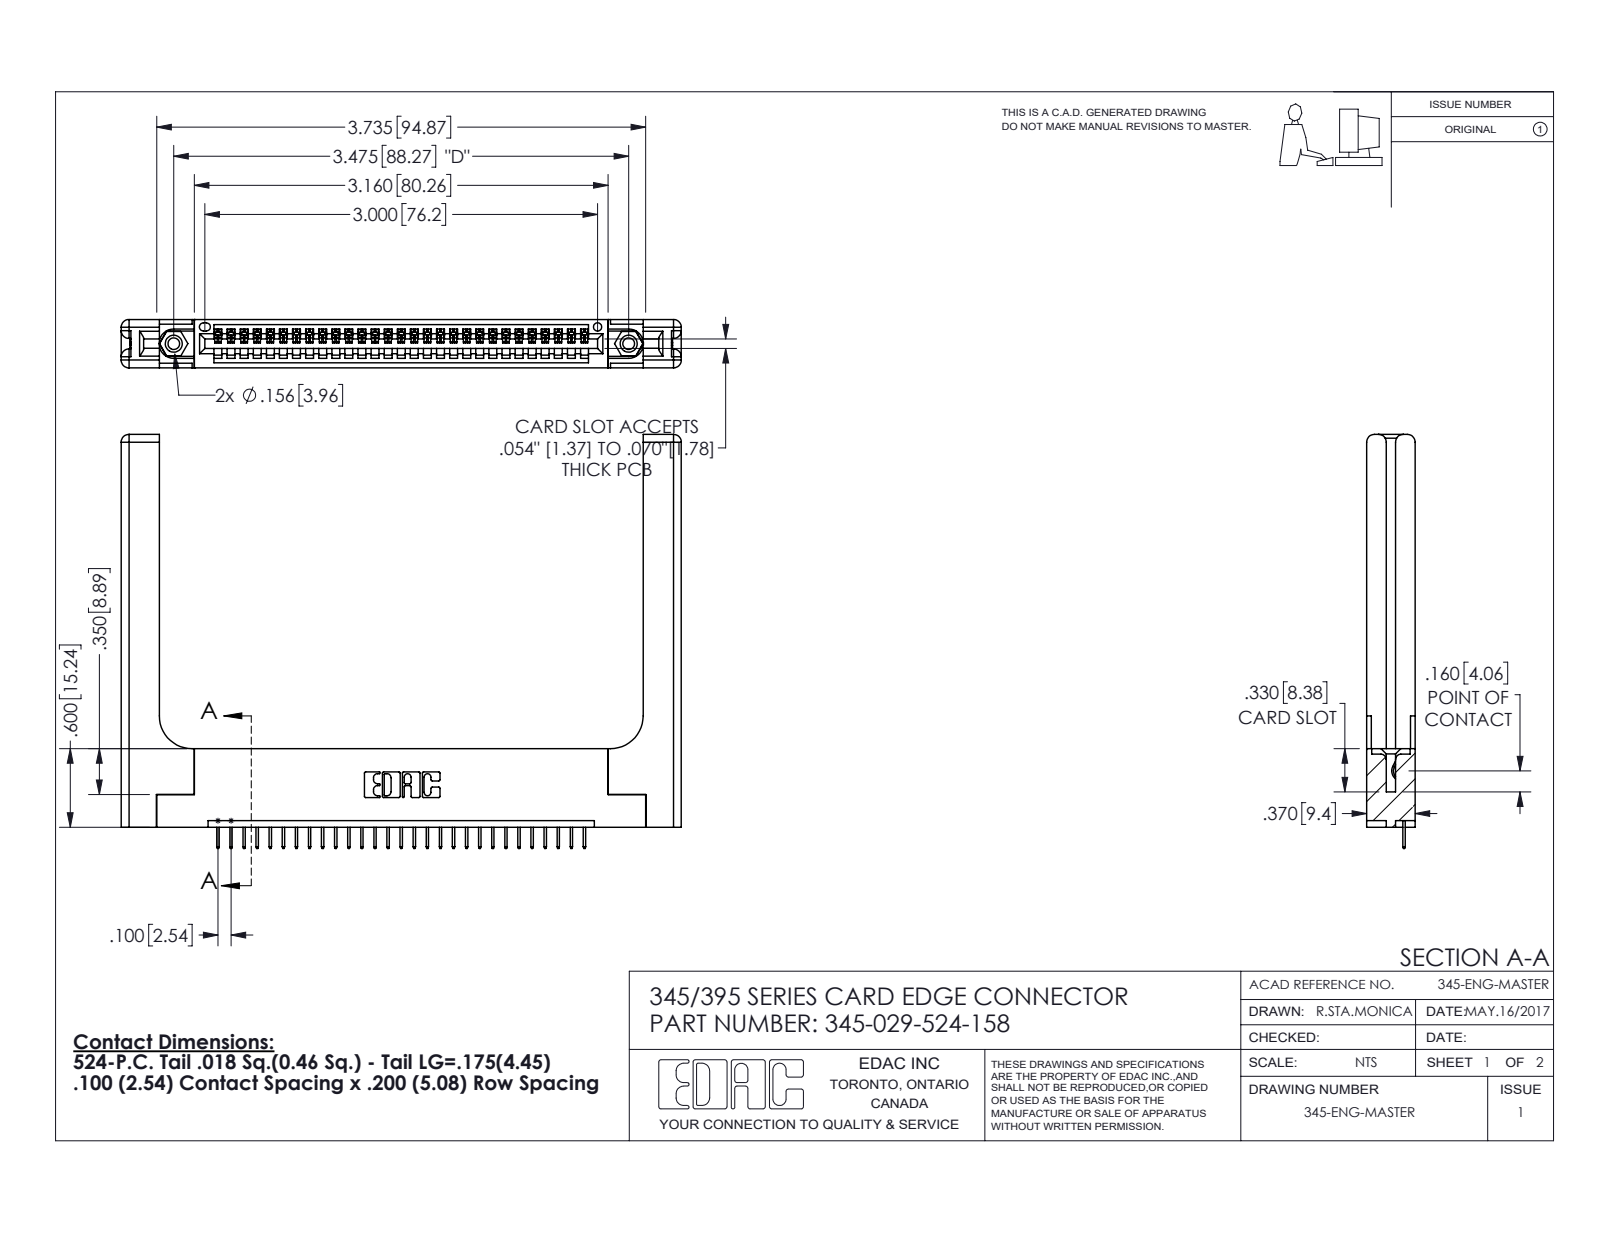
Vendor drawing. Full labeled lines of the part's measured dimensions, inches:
Part name (STEP PRODUCT): 345-029-524-158; 345 Part_Flush Mounting Lugs - 0.156 Dia-TH; 345-220-058_345-220-058; 345-250-001_345-250-001-102 (+1 more)
STEP written by: SolidWorks 2016 (CONFIG_CONTROL_DESIGN)
Units: inches
Bodies: 34 solids, 2180 faces (1562 planar, 558 cylindrical, 60 other)
Overall size (bounding box): 4.279 × 3.162 × 0.37
Volume: 1.135 in³ · Surface area: 28.19 in²
Round holes (diameter × count): ⌀0.089 ×2, ⌀0.125 ×2, ⌀0.156 ×2, ⌀0.064 ×1
Round bosses / shafts (diameter × count): ⌀0.155 ×2
Partial cylindrical surfaces — rounded edges, fillets, slot ends (radius × count): R0.006 ×58, R0.01 ×22, R0.06 ×16, R0.007 ×6, R0.031 ×6, R0.026 ×3, R0.03 ×2, R0.031 ×2
Main face-to-face distances: 0.37, 0.072, 0.298, 0.2, 0.148, 0.15, 0.098, 0.272, 0.025, 0.077
Hole centre spacings: 0.27, 3.24, 3.475
